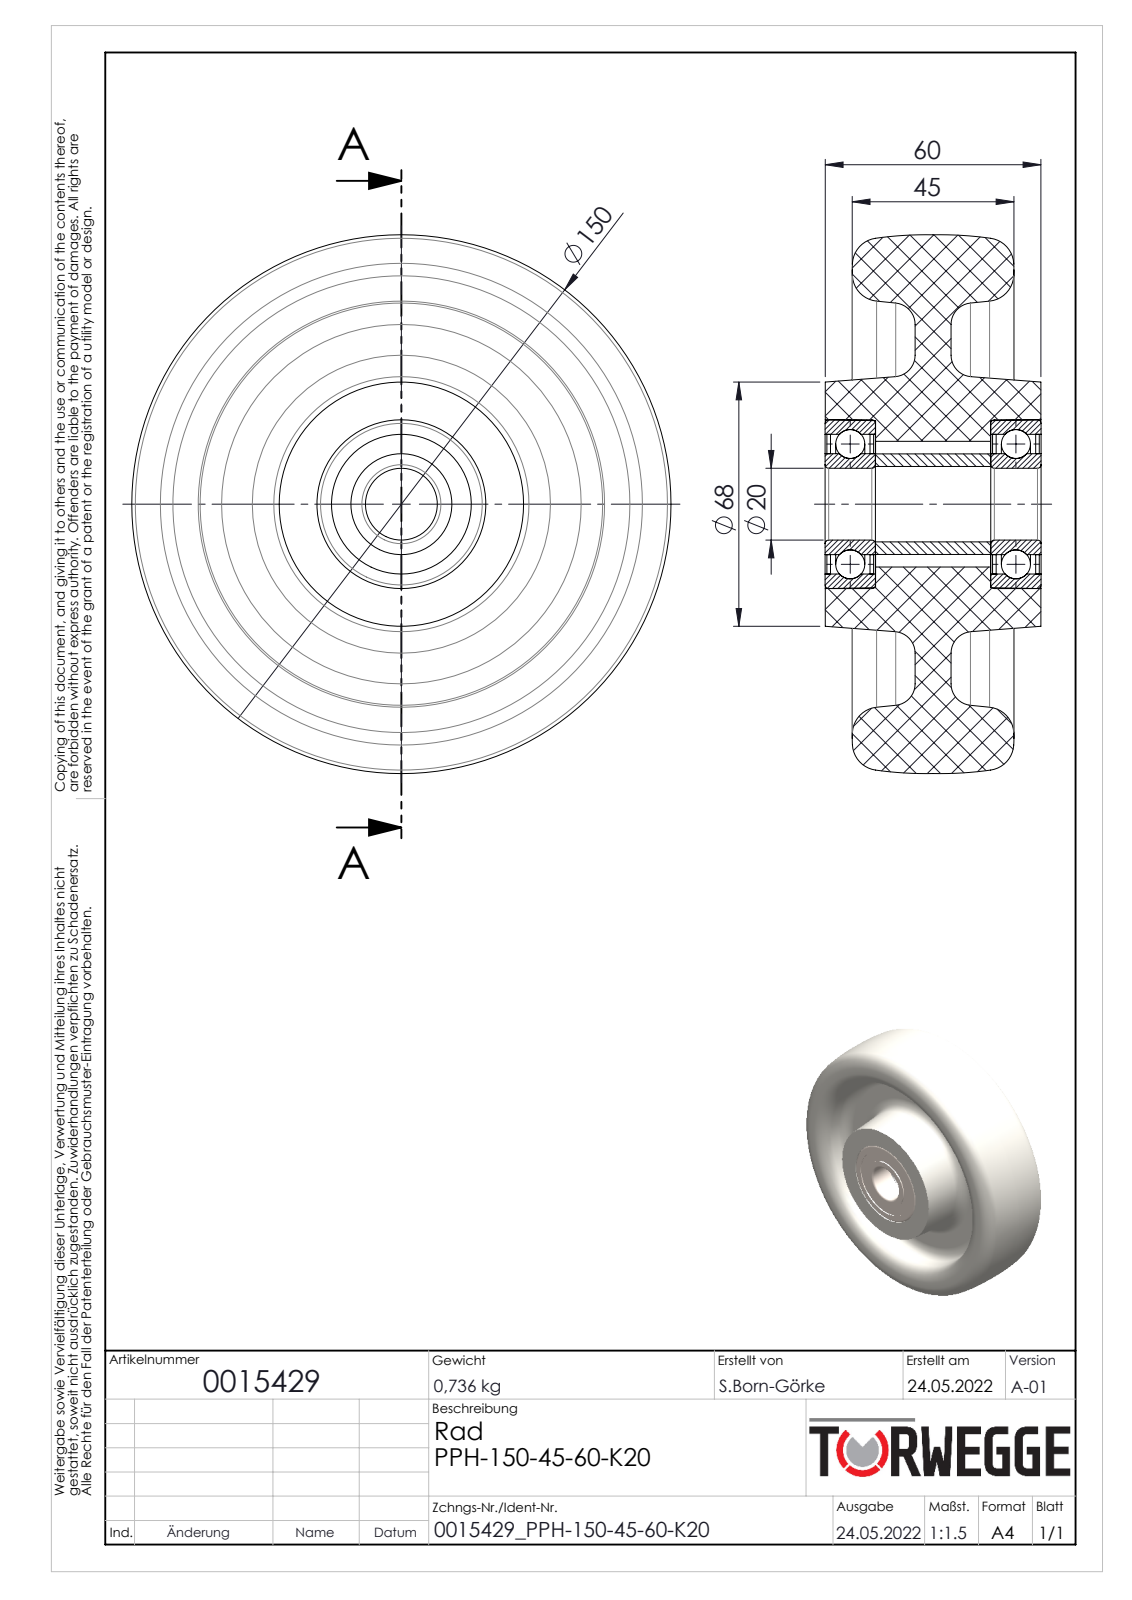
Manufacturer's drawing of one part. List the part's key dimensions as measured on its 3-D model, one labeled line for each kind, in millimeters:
Part name (STEP PRODUCT): 0015429
STEP written by: SolidWorks 2020 (AUTOMOTIVE_DESIGN)
Units: millimetres
Bodies: 12 solids, 142 faces (24 planar, 46 cylindrical, 72 other)
Overall size (bounding box): 150.04 × 150.04 × 60.1
Volume: 581 871 mm³ · Surface area: 106 746 mm²
Round holes (diameter × count): ⌀20 ×1, ⌀21 ×1, ⌀28.1 ×1, ⌀35 ×1, ⌀38.9 ×1
Round bosses / shafts (diameter × count): ⌀47 ×1, ⌀28 ×1
Main face-to-face distances: 25, 35, 46.1, 46.05, 14, 11, 10, 0.5, 1.5, 12.5
